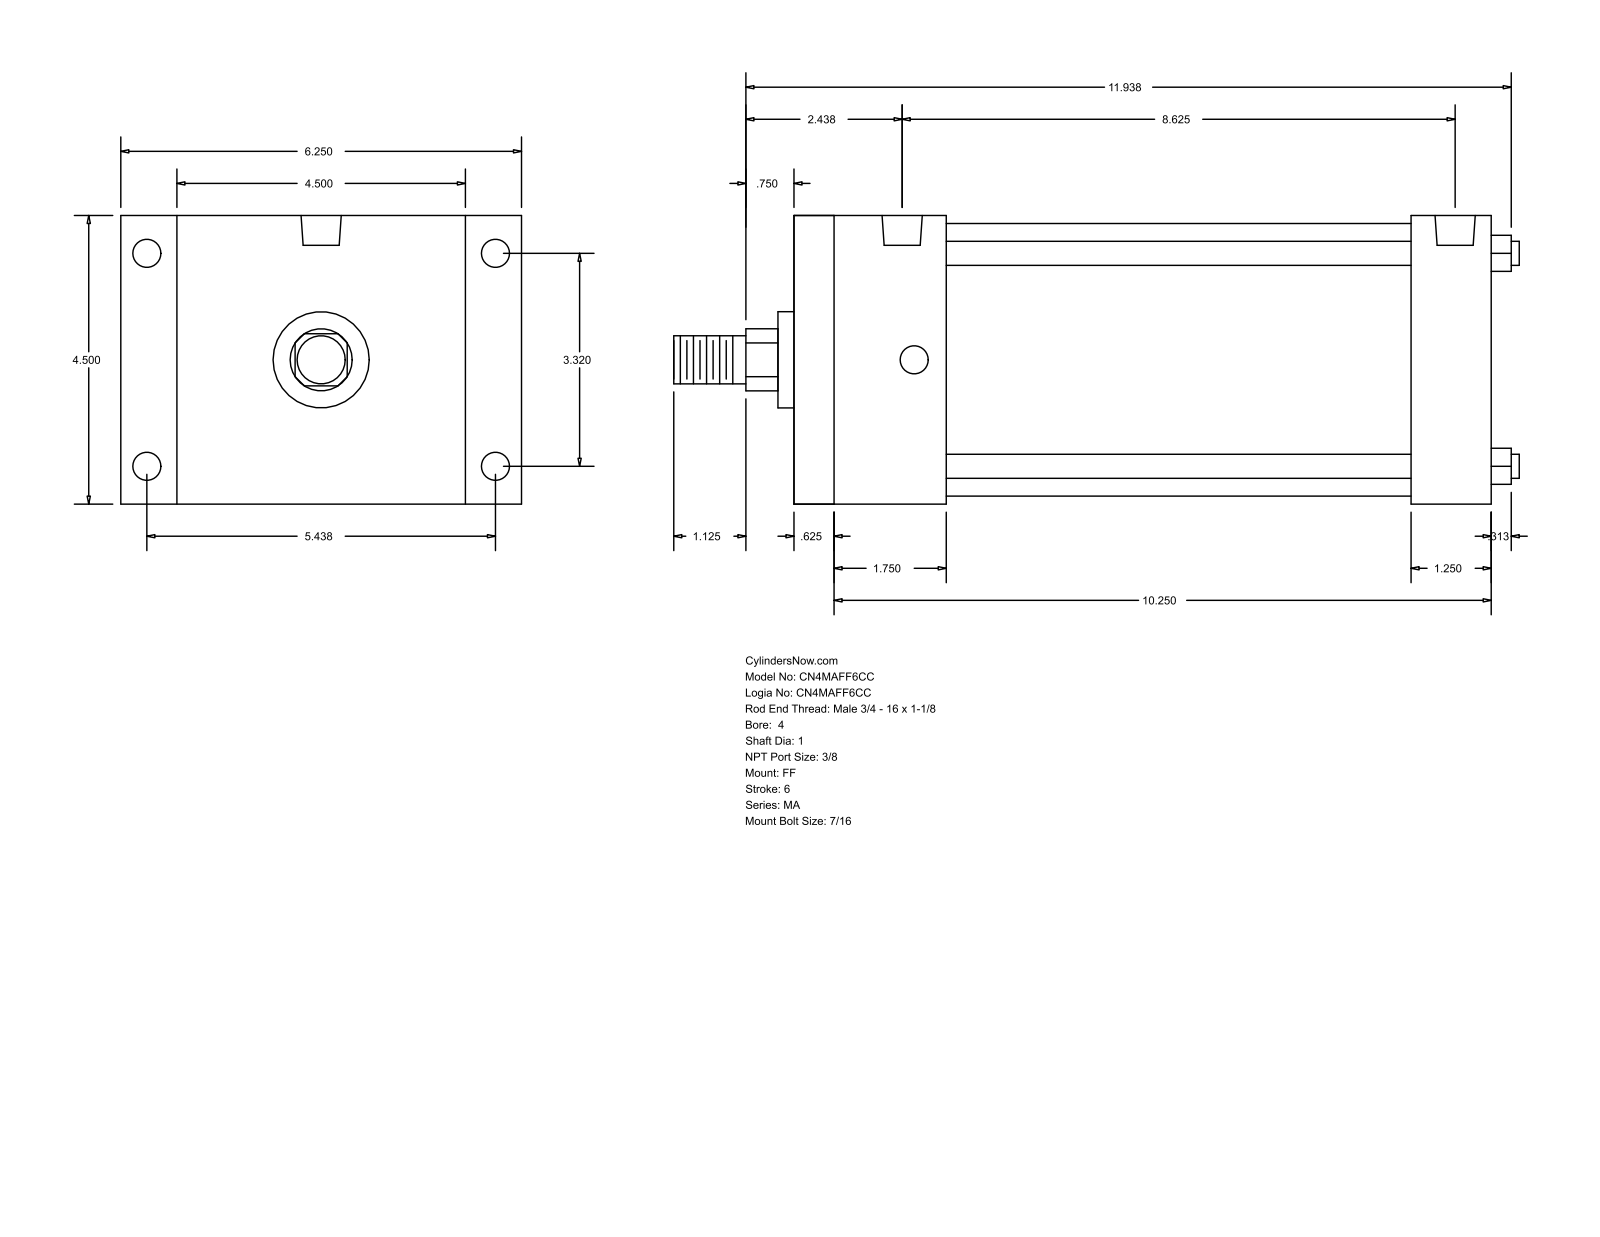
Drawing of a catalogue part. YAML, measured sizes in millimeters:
part_name: "MA_FF__0400_1"
step_written_by: "GSSL Pune (CONFIG_CONTROL_DESIGN)"
units: millimeters
bodies: {solids: 0, faces: 92, planar: 64, cylindrical: 28, other: 0}
overall_size: [334.96, 158.75, 114.3]
round_holes:
  - {diameter: 11.11, count: 8}
  - {diameter: 15.93, count: 2}
round_bosses_or_shafts:
  - {diameter: 9.53, count: 4}
  - {diameter: 107.95, count: 1}
  - {diameter: 38.1, count: 1}
  - {diameter: 25.4, count: 1}
  - {diameter: 19.05, count: 1}
partial_cylinders:
  - {radius: 12.29, count: 1}
face_to_face_distances: [114.3, 276.22, 15.87, 260.35, 22.23, 136.53, 244.47, 228.6, 31.75, 60.33]
hole_center_spacings: [4.76, 84.32, 138.12, 161.82, 209.56, 214.32, 219.08]
